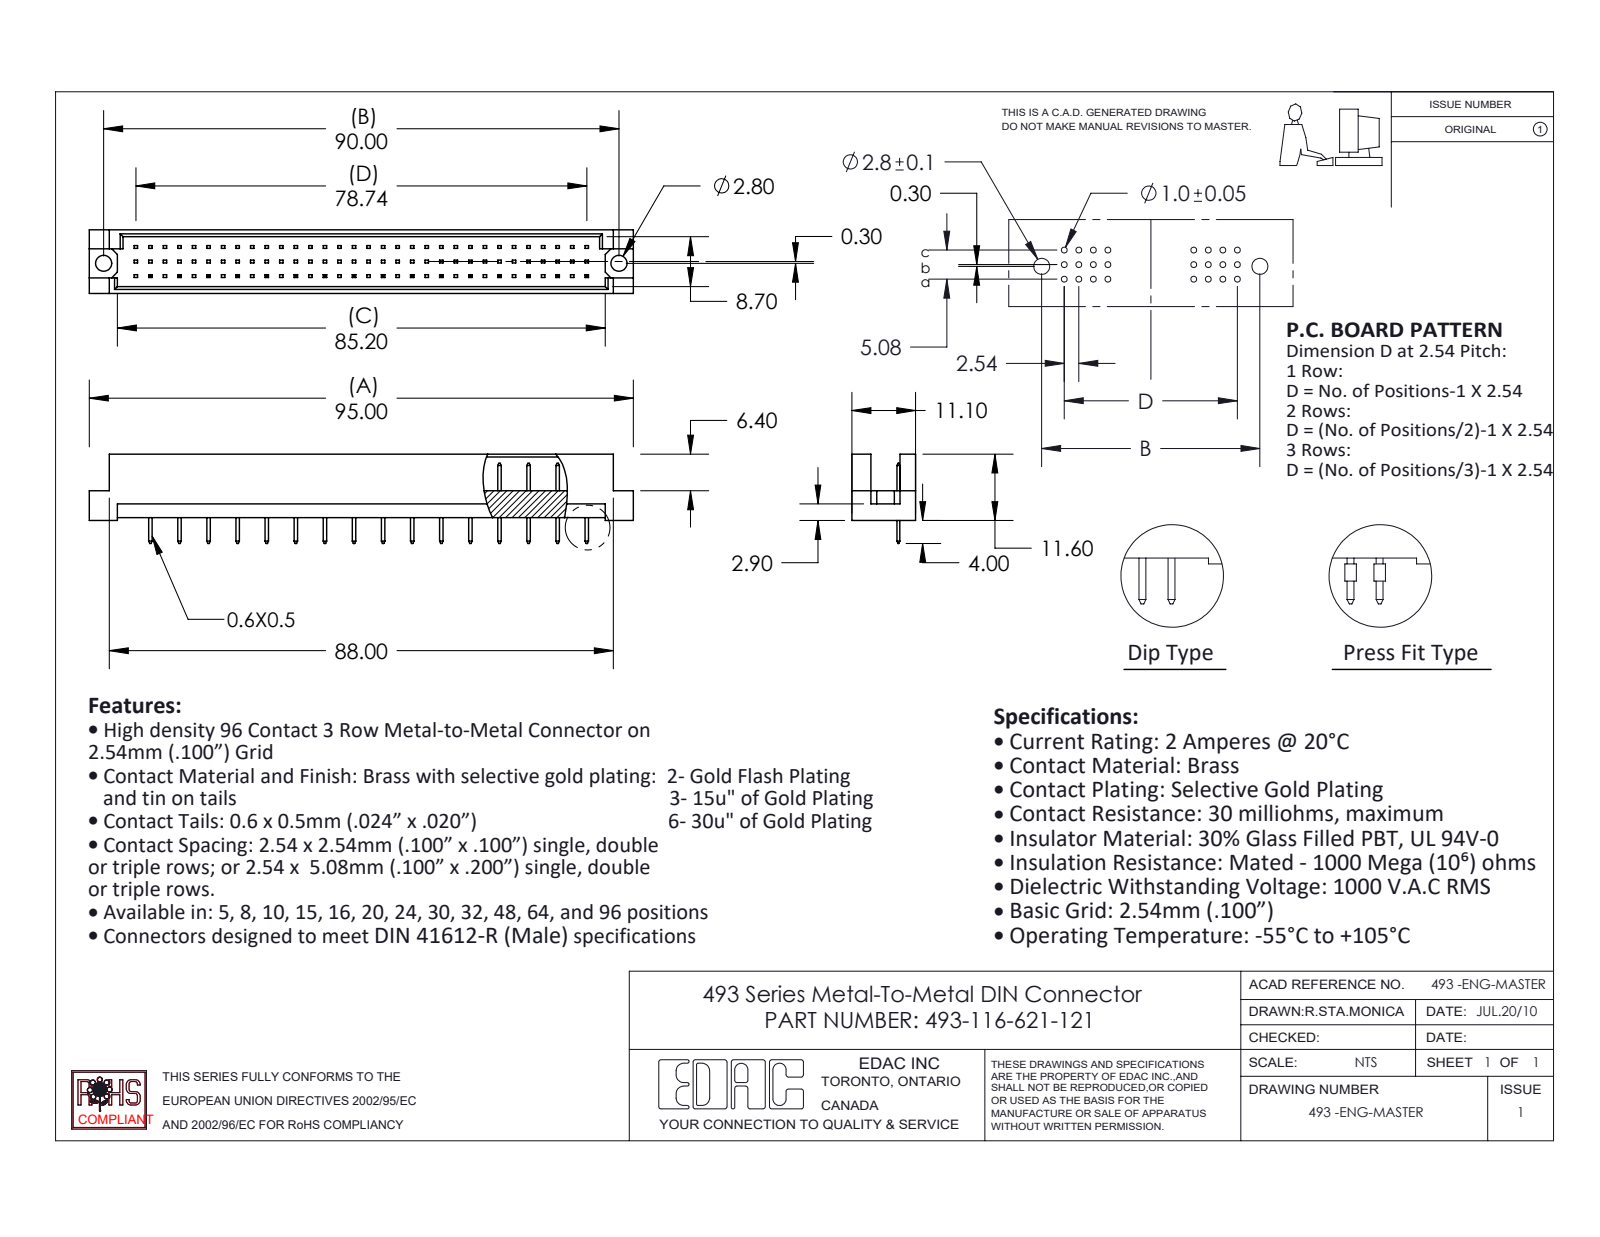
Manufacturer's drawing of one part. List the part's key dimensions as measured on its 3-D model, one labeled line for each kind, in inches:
Part name (STEP PRODUCT): 493-290_21; 493 Part_96; 493-116-621-122
STEP written by: SolidWorks 2020 (CONFIG_CONTROL_DESIGN)
Units: inches
Bodies: 17 solids, 660 faces (656 planar, 4 cylindrical, 0 other)
Overall size (bounding box): 3.74 × 0.614 × 0.437
Volume: 0.349 in³ · Surface area: 10.79 in²
Round holes (diameter × count): ⌀0.11 ×2
Main face-to-face distances: 0.047, 0.39, 0.437, 0.343, 0.185, 0.02, 0.2, 0.1, 0.109, 0.328
Hole centre spacings: 3.543
